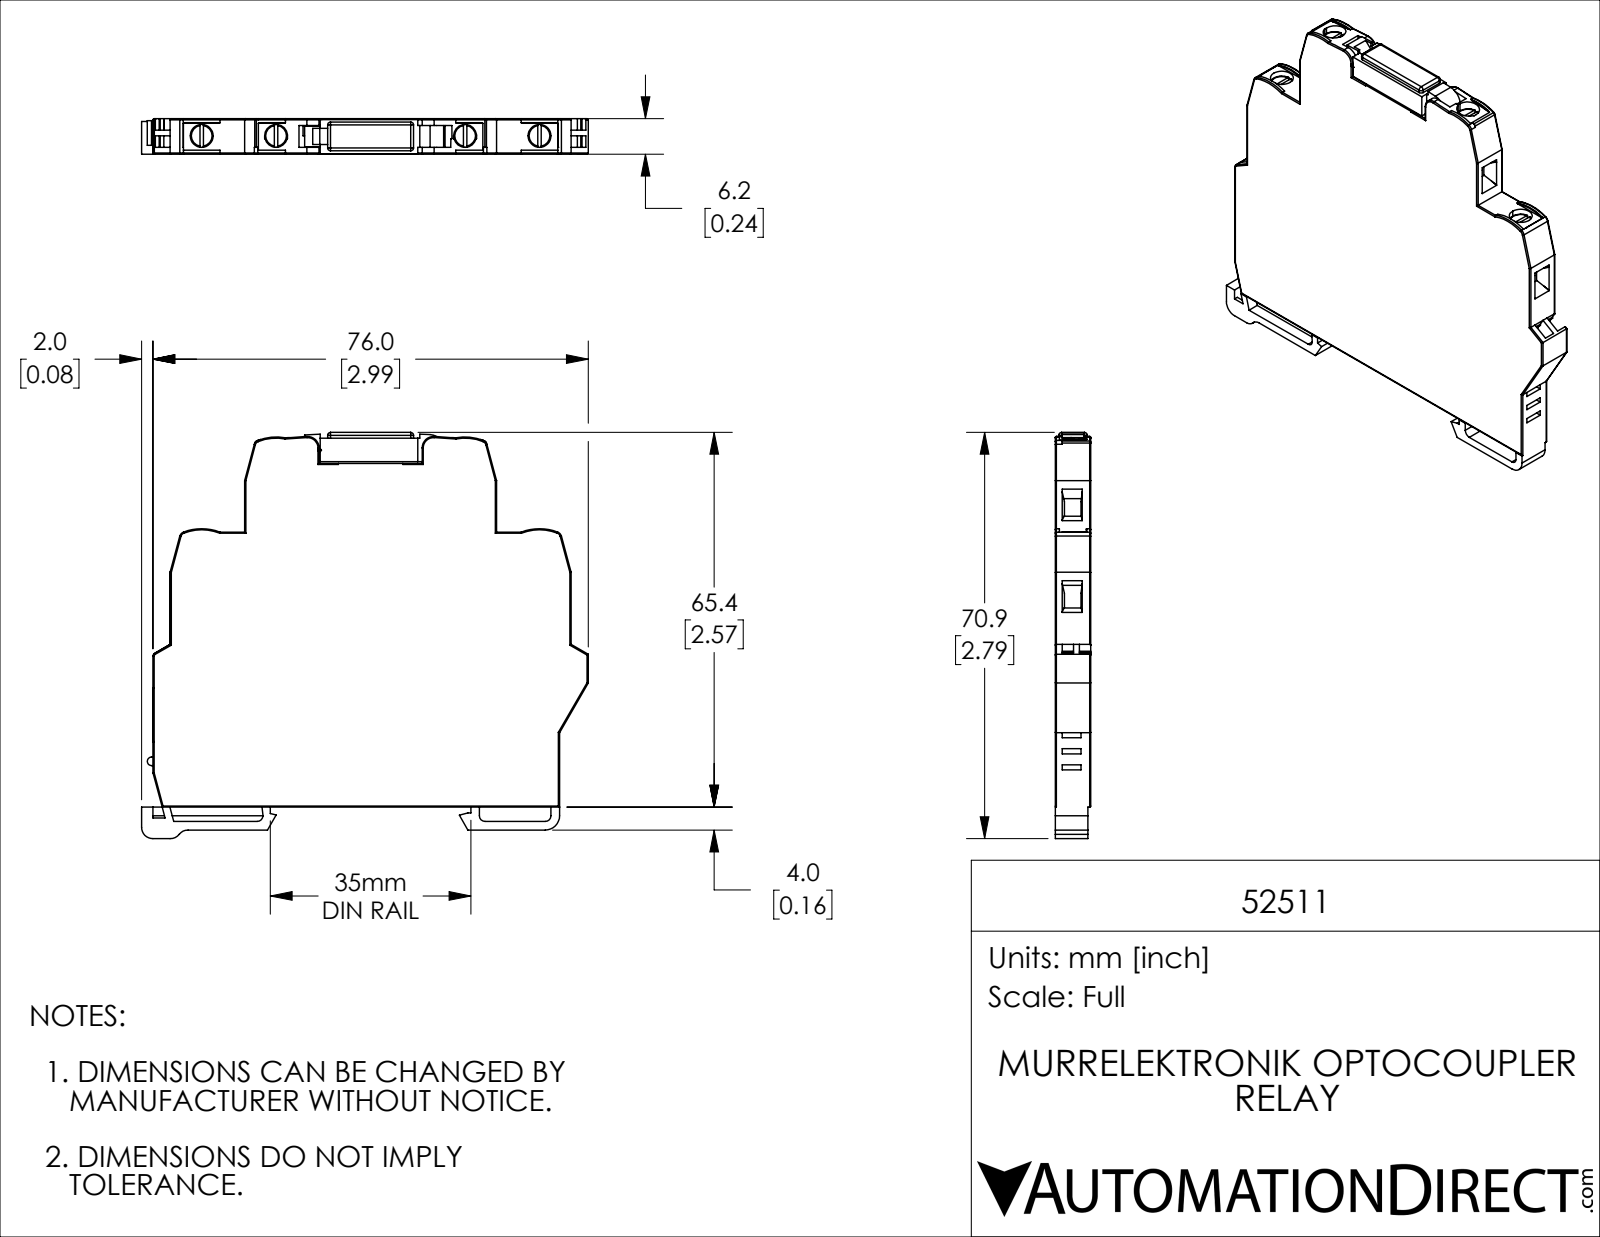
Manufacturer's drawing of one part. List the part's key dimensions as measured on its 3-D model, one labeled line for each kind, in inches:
Part name (STEP PRODUCT): 52511
STEP written by: SolidWorks 2019 (CONFIG_CONTROL_DESIGN)
Units: inches
Bodies: 2 solids, 496 faces (298 planar, 138 cylindrical, 60 other)
Overall size (bounding box): 3.071 × 2.791 × 0.244
Volume: 1.561 in³ · Surface area: 18.26 in²
Round holes (diameter × count): ⌀0.157 ×4, ⌀0.075 ×1
Round bosses / shafts (diameter × count): ⌀0.079 ×1
Partial cylindrical surfaces — rounded edges, fillets, slot ends (radius × count): R0.008 ×50, R0.02 ×11, R0.039 ×7, R0.079 ×6, R0.03 ×5, R0.005 ×4, R0.346 ×4, R0.016 ×3
Main face-to-face distances: 0.244, 0.059, 0.197, 0.118, 0.098, 2.362, 0.157, 0.079, 0.047, 0.02
Hole centre spacings: 0.512, 1.811, 1.299, 2.323
